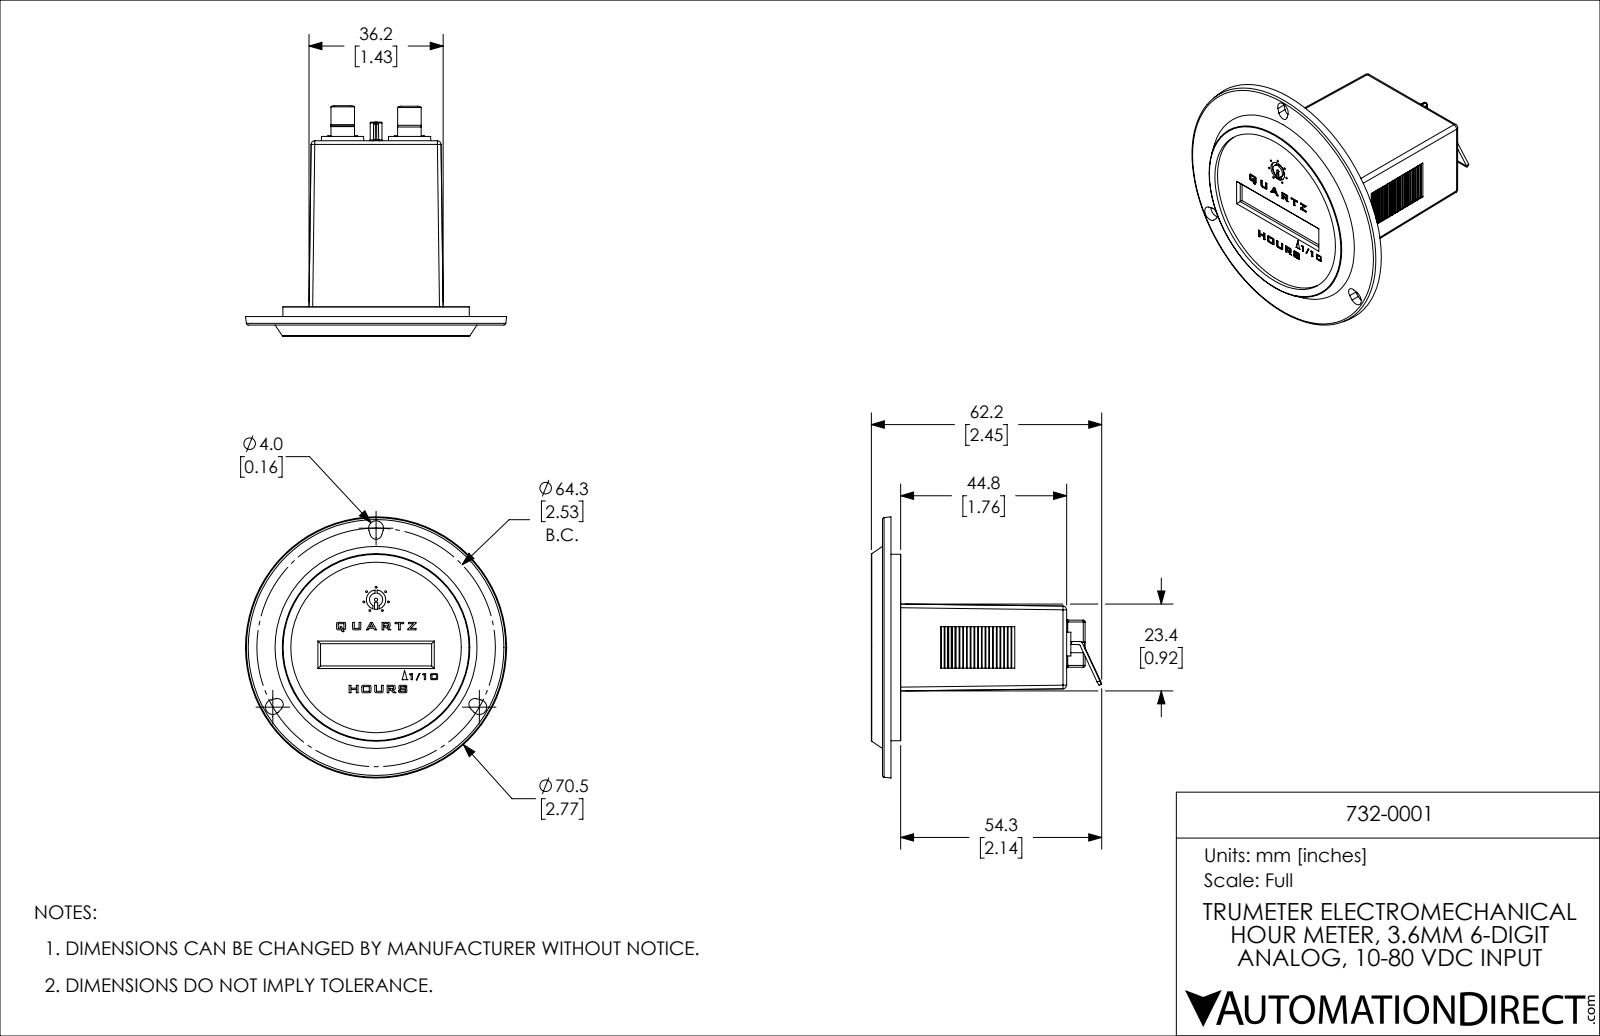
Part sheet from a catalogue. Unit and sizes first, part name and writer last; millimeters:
Units: millimetres
Overall size (bounding box): 70.46 × 70.46 × 62.16
Round holes (diameter × count): ⌀0.5 ×7, ⌀1.5 ×4, ⌀0.84 ×1, ⌀5.26 ×1, ⌀46 ×1
Round bosses / shafts (diameter × count): ⌀50.3 ×1, ⌀3.58 ×1
Partial cylindrical surfaces — rounded edges, fillets, slot ends (radius × count): R0.5 ×30, R1 ×17, R0.3 ×15, R1.5 ×6, R0.35 ×4, R1.75 ×4, R2.5 ×4, R1.6 ×3
Main face-to-face distances: 2, 2.9, 2.3, 4.3, 0.6, 1.4, 2.4, 3, 4.9, 1.9
Hole centre spacings: 3.36, 2.85, 6.5, 5.16, 2.84, 3.37, 5.15, 5.51
Volume: 19 947 mm³ · Surface area: 24 460 mm²
Bodies: 1 solid, 749 faces (557 planar, 138 cylindrical, 54 other)
Part name (STEP PRODUCT): 732-0001
STEP written by: SolidWorks 2021 (CONFIG_CONTROL_DESIGN)
